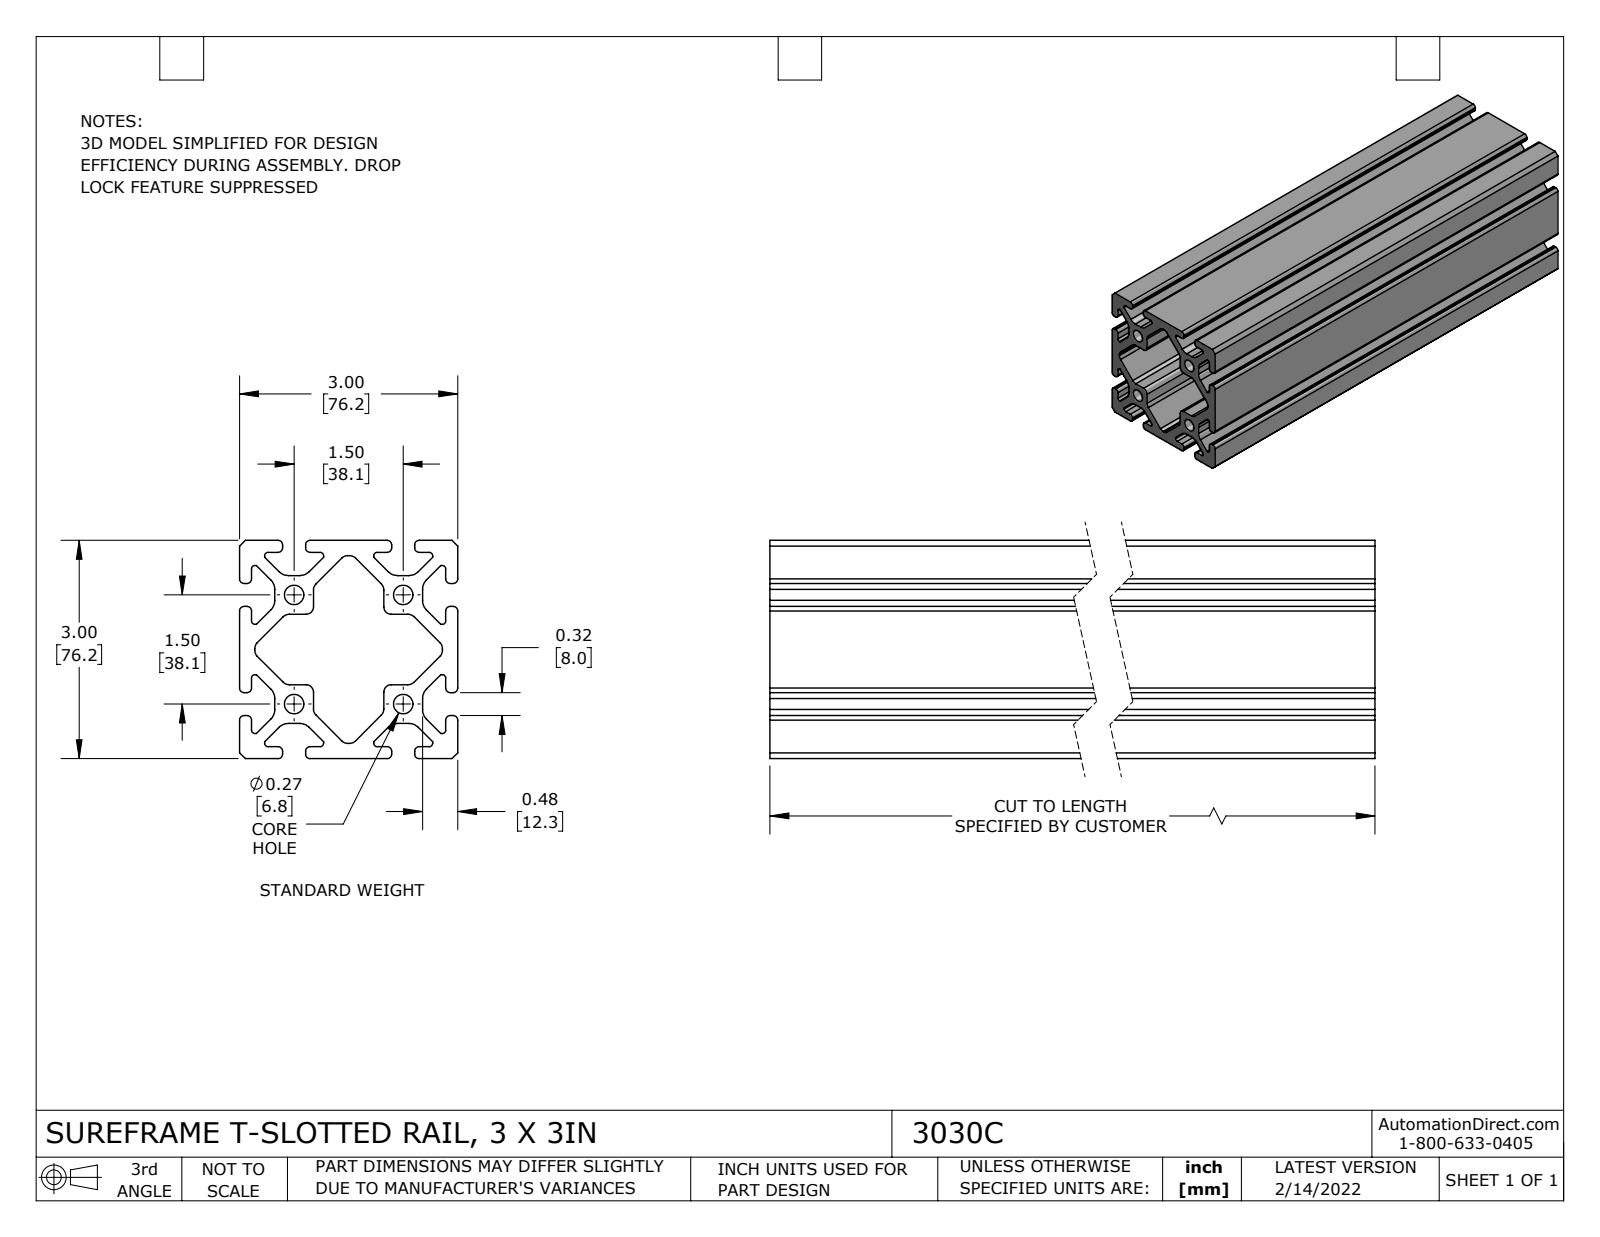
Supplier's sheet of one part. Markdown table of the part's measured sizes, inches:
| quantity | value |
| --- | --- |
| part name | 3030C |
| STEP written by | SolidWorks 2021 (CONFIG_CONTROL_DESIGN) |
| units | inches |
| bodies | 1 solid, 202 faces (110 planar, 92 cylindrical, 0 other) |
| overall size | 10 × 3 × 3 |
| volume | 34.36 in³ |
| surface area | 359.2 in² |
| round holes (diameter × count) | 0.268 × 4 |
| partial cylindrical surfaces (radius × count) | 0.047 × 16, 0.062 × 16, 0.063 × 16, 0.187 × 15, 0.115 × 8, 0.125 × 8, 0.1 × 4, 0.188 × 1 |
| main face-to-face distances | 3, 0.874, 1.034, 0.186, 1.061, 1.22, 2.095, 0.165, 2.835, 1.909 |
| hole center spacings | 1.5, 2.121 |
